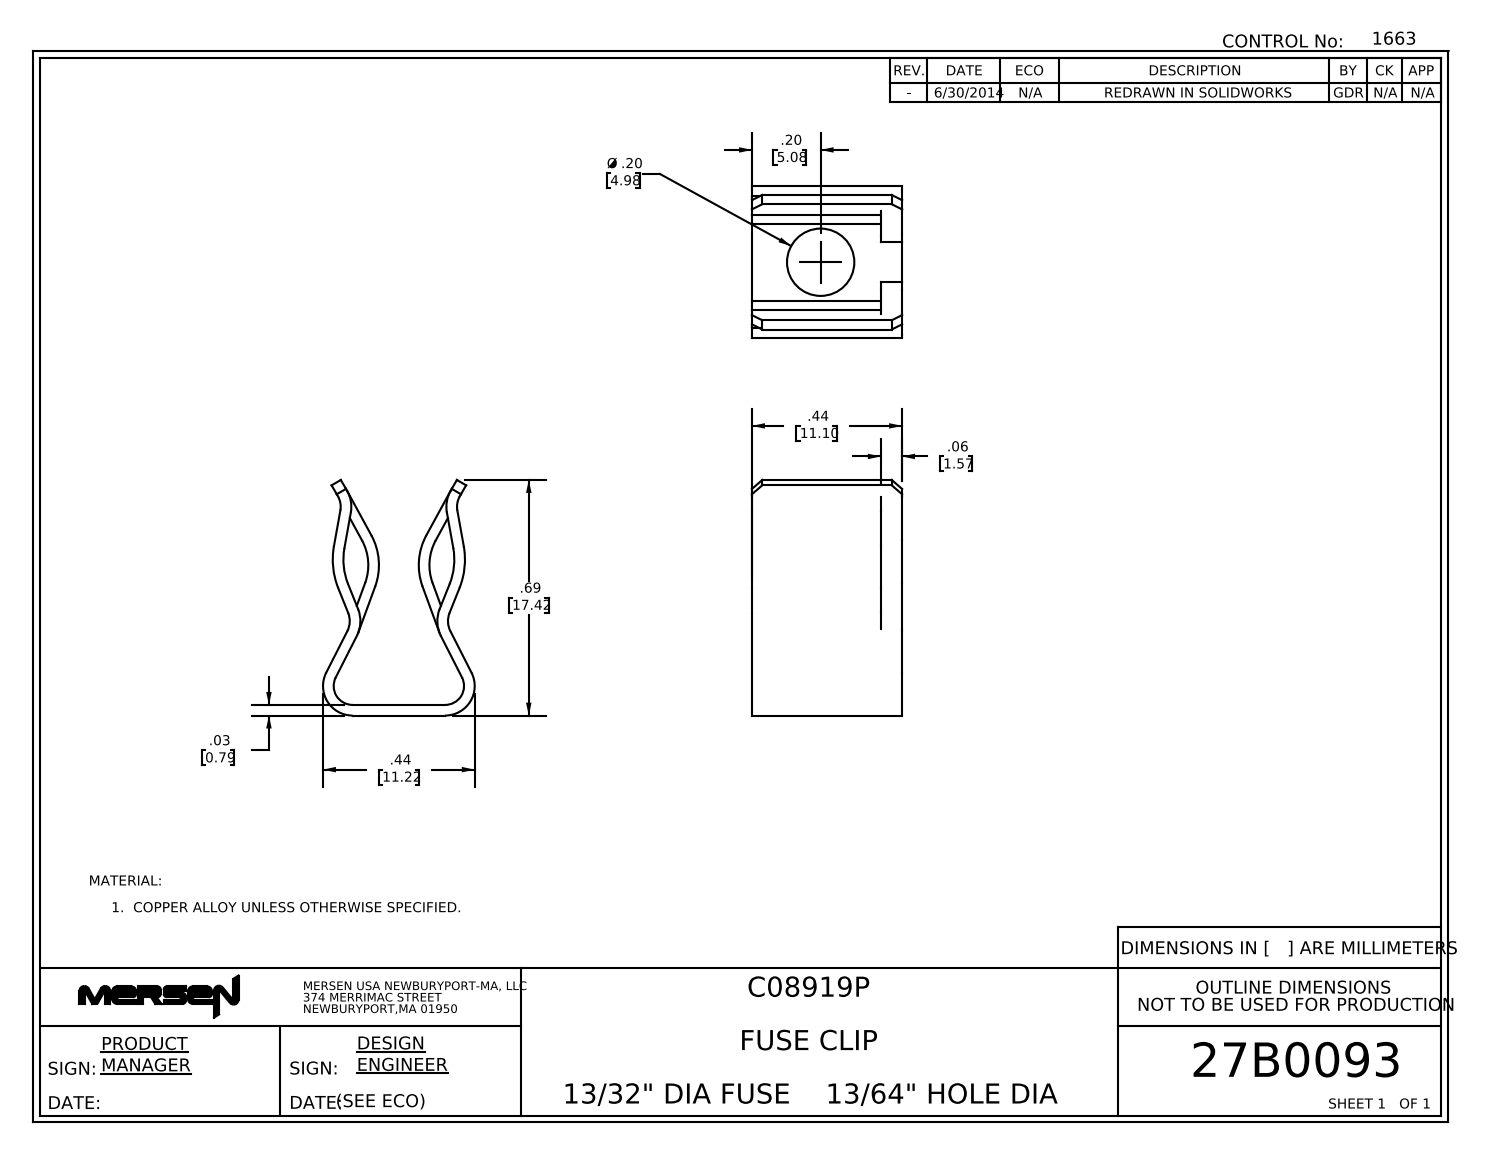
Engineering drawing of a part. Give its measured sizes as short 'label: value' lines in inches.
name: 27B0093rev
written by: SolidWorks 2017 (AUTOMOTIVE_DESIGN)
unit: in
bodies: 1 solid, 83 faces (62 planar, 21 cylindrical, 0 other)
size: 0.686 × 0.442 × 0.437
volume: 0.023 in³; area: 1.658 in²
holes: 1× ⌀0.196
rounds: 2× R0.055, 2× R0.062, 2× R0.064, 2× R0.086, 2× R0.093, 2× R0.095, 2× R0.151, 2× R0.182
face distances: 0.031, 0.031, 0.437, 0.375, 0.062, 0.375, 0.437
